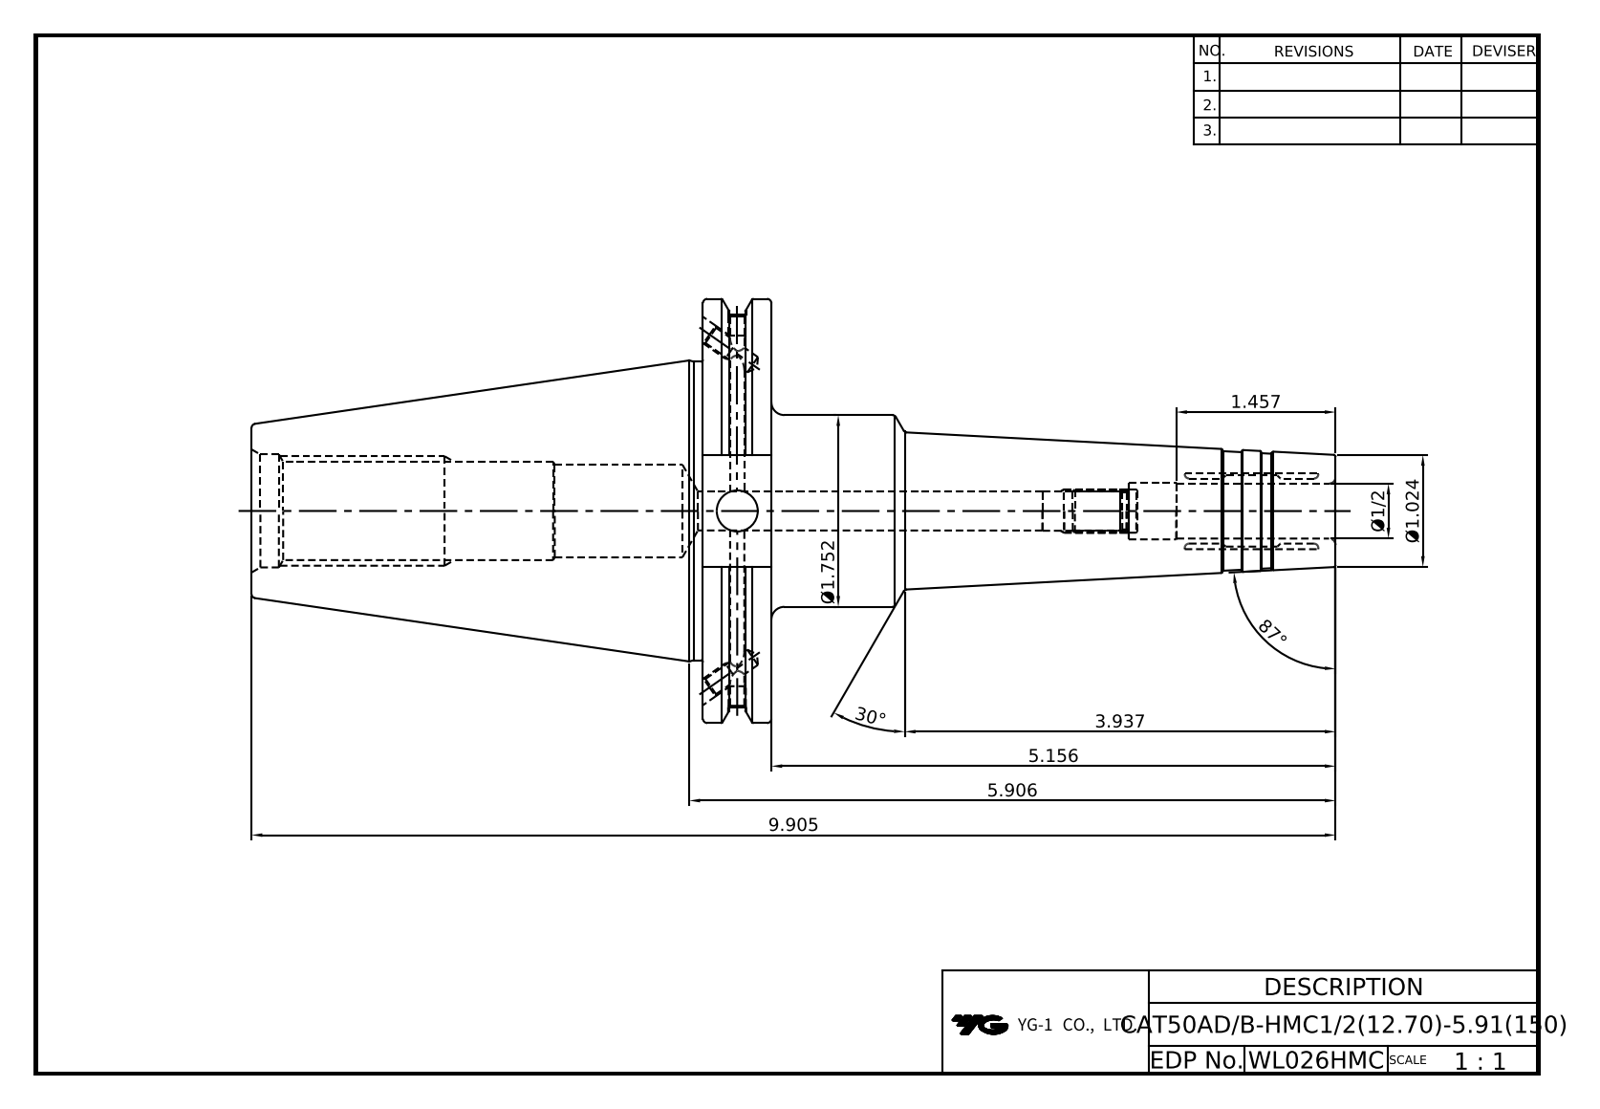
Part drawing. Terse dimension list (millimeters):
name: CAT50ADB-HMC12.7-150
written by: Autodesk Inventor 2020 (AUTOMOTIVE_DESIGN)
unit: mm
bodies: 1 solid, 104 faces (37 planar, 27 cylindrical, 40 other)
size: 251.6 × 98.42 × 94.69
volume: 437 739 mm³; area: 62 016 mm²
holes: 2× ⌀3.24, 2× ⌀4.13, 2× ⌀4.2, 2× ⌀5, 1× ⌀9, 1× ⌀9.53, 1× ⌀12.7, 1× ⌀13.2, 1× ⌀21.5, 1× ⌀21.97, 1× ⌀26.2
bosses: 1× ⌀98.42, 1× ⌀91.29, 1× ⌀69.25, 1× ⌀44.5
face distances: 15.88, 104.77, 120.65, 251.6, 146.83, 130.95, 73.03, 25.9, 110.82, 6.05
